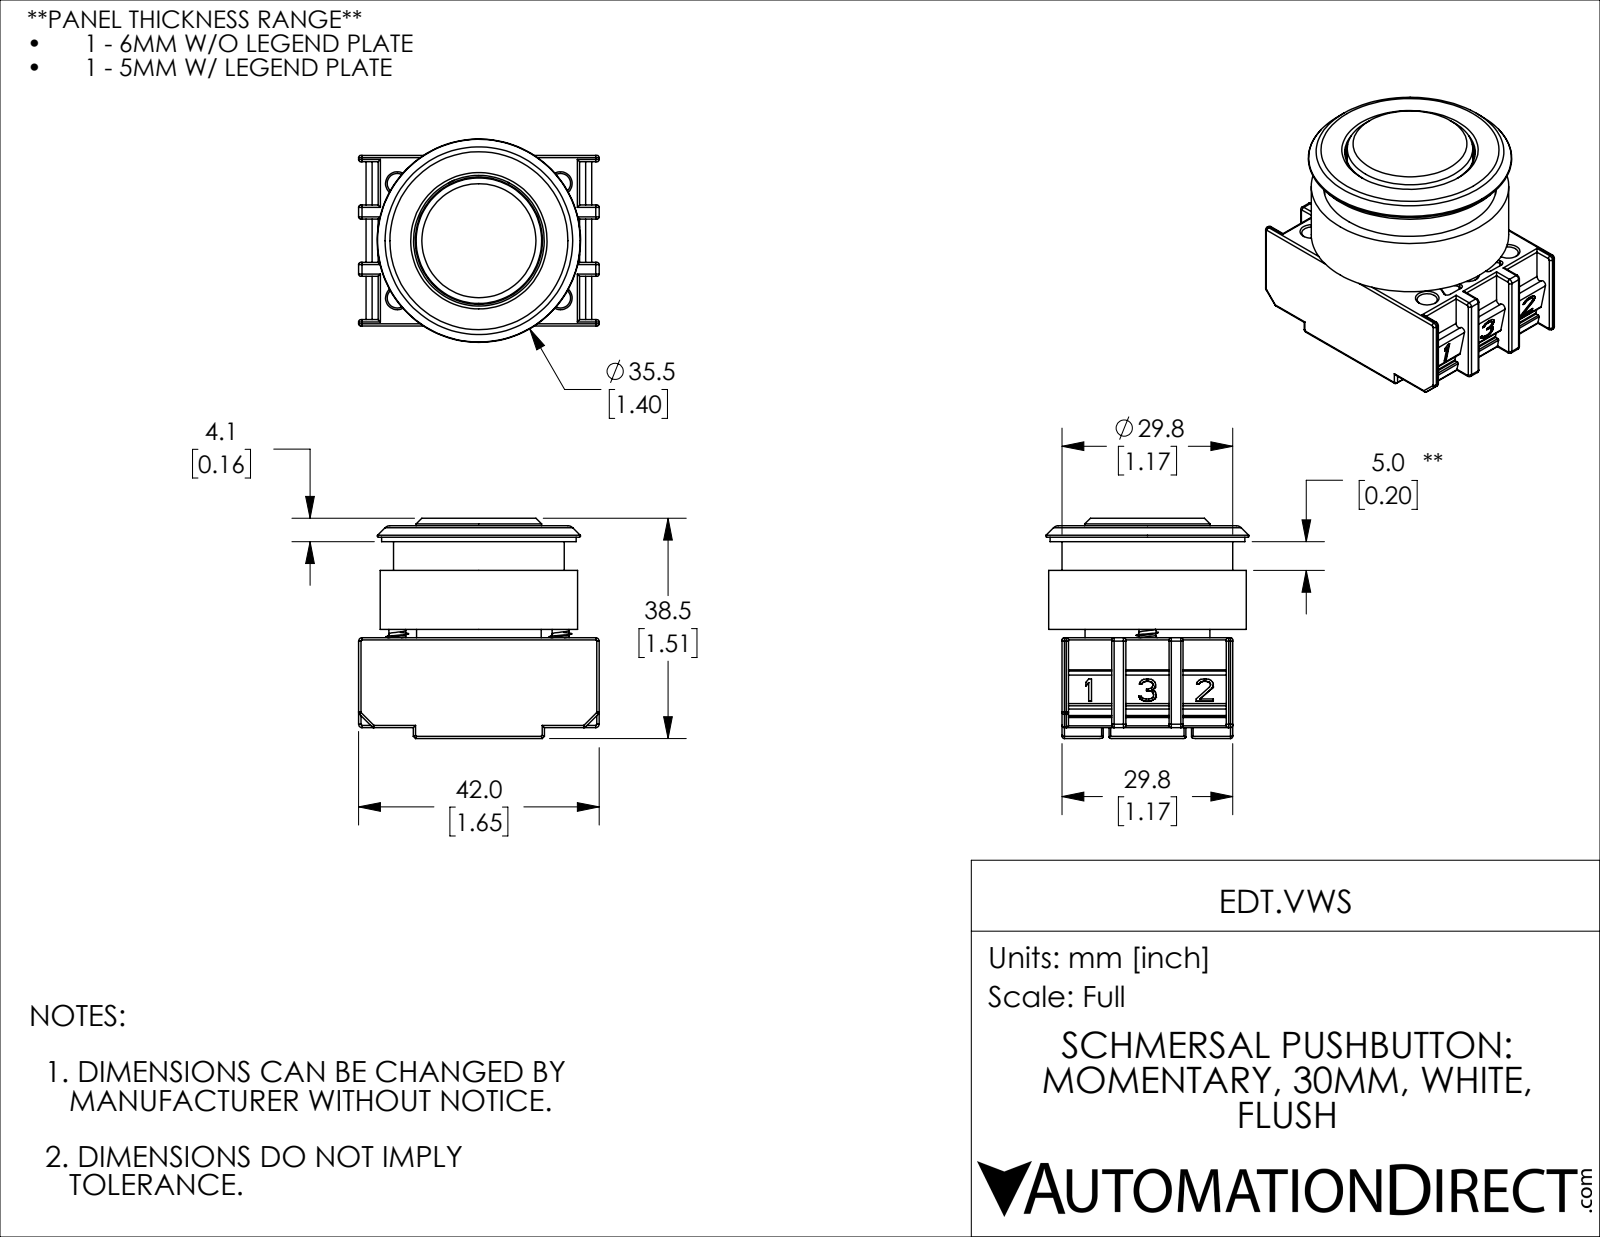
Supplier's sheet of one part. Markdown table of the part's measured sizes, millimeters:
| quantity | value |
| --- | --- |
| part name | EDT.VWS |
| STEP written by | SolidWorks 2019 (CONFIG_CONTROL_DESIGN) |
| units | millimeters |
| bodies | 3 solids, 1361 faces (509 planar, 460 cylindrical, 392 other) |
| overall size | 42 × 38.45 × 35.5 |
| volume | 22 602 mm³ |
| surface area | 20 491 mm² |
| round holes (diameter × count) | 3.5 × 6, 5.15 × 6, 4.1 × 1, 12.5 × 1, 18 × 1, 19.2 × 1, 22.2 × 1, 22.8 × 1, 24.2 × 1, 26 × 1, 27 × 1, 30.2 × 1 |
| round bosses / shafts (diameter × count) | 4.8 × 2, 2.93 × 2, 34.5 × 1, 34 × 1, 29.8 × 1, 24.6 × 1, 21.9 × 1, 21.8 × 1 |
| partial cylindrical surfaces (radius × count) | 0.4 × 112, 0.3 × 48, 0.2 × 24, 0.6 × 8, 0.5 × 6, 0.1 × 2, 0.6 × 2, 0.8 × 2 |
| main face-to-face distances | 29.8, 1.9, 19.4, 5.9, 4.1, 1.45, 16.2, 19.05, 10, 1.3 |
| hole center spacings | 10, 17.41, 30.2, 28.5, 14.25, 20, 34.82 |
